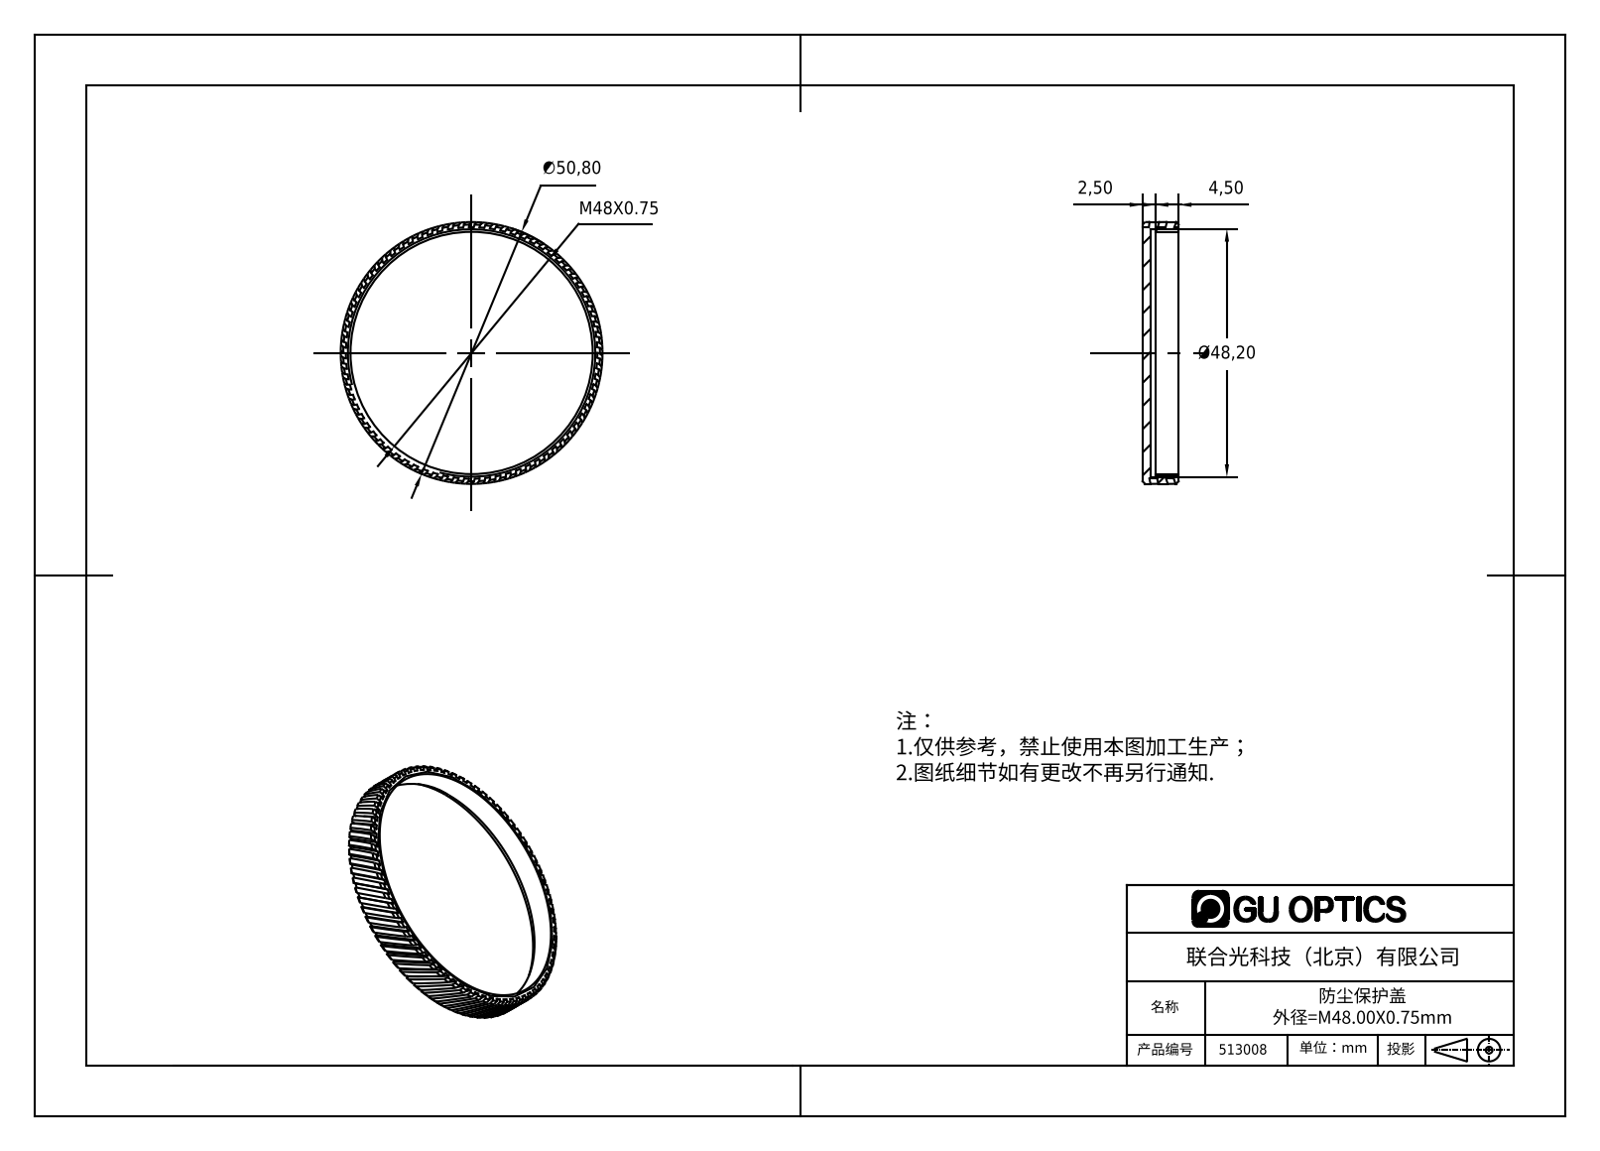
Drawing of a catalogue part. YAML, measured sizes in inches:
part_name: "513008"
step_written_by: "SolidWorks 2016 (AUTOMOTIVE_DESIGN)"
units: inches
bodies: {solids: 1, faces: 462, planar: 154, cylindrical: 156, other: 152}
overall_size: [2, 2, 0.276]
volume: 0.246
surface_area: 11.13
round_holes:
  - {diameter: 1.85, count: 1}
  - {diameter: 1.898, count: 1}
round_bosses_or_shafts:
  - {diameter: 2, count: 1}
  - {diameter: 1.921, count: 1}
face_to_face_distances: [0.059, 0.031, 0.217, 0.276, 0.177, 0.039, 0.098, 0.032, 0.031]
